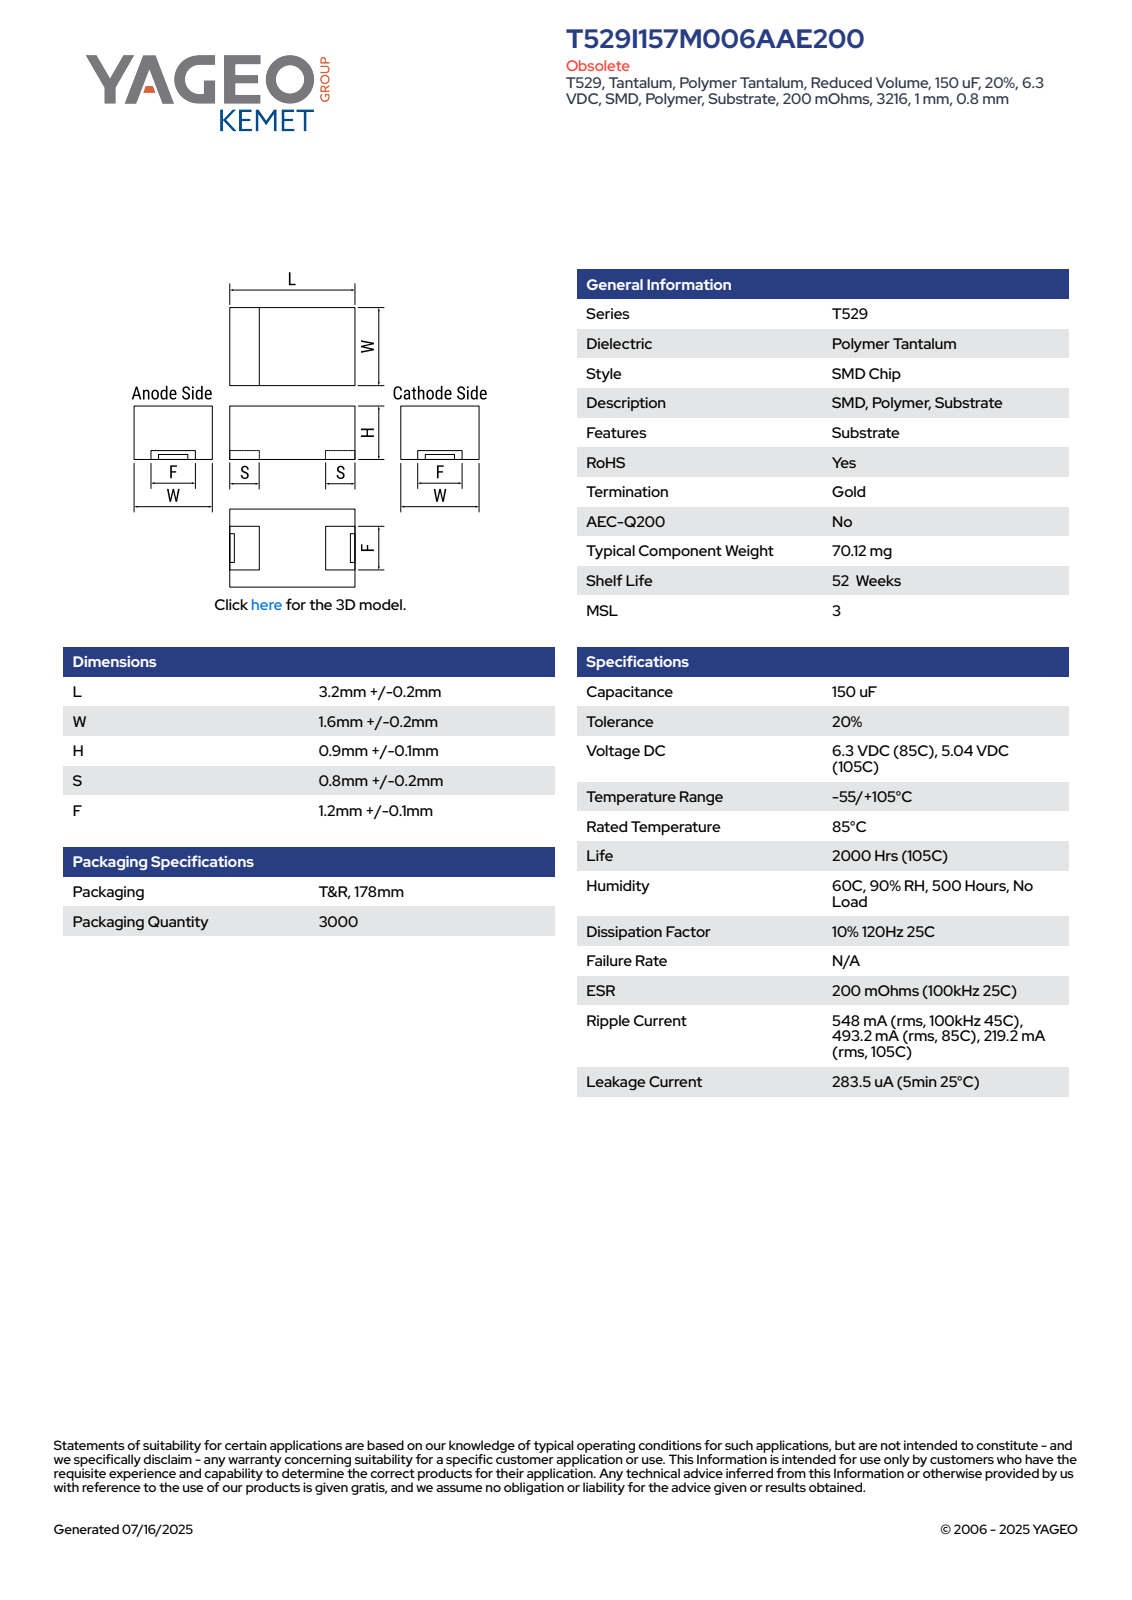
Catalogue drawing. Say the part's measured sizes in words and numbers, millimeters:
The part is named "Ta_SMT_P-Case_SubstrateBoard3216; CTSss3216I_L3.2W1.6H1S0.8F1.2; T529_P-Case3216; Ta_SMT_P-Case_Anode+3216 (+1 more)". Its 3-D file was written by "SolidWorks 2014 (AUTOMOTIVE_DESIGN)". It is 7 solids with 127 faces: 113 planar, 10 cylindrical and 4 other. Overall it measures 3.4 by 1.8 by 1 millimeters. Its volume is 6 cubic millimeters and its surface area 39 square millimeters. The main face-to-face distances are 0.9, 1, 1.8, 0.95, 3.4, 0.94, 0.85, 1.5, 3.25, 0.8.
